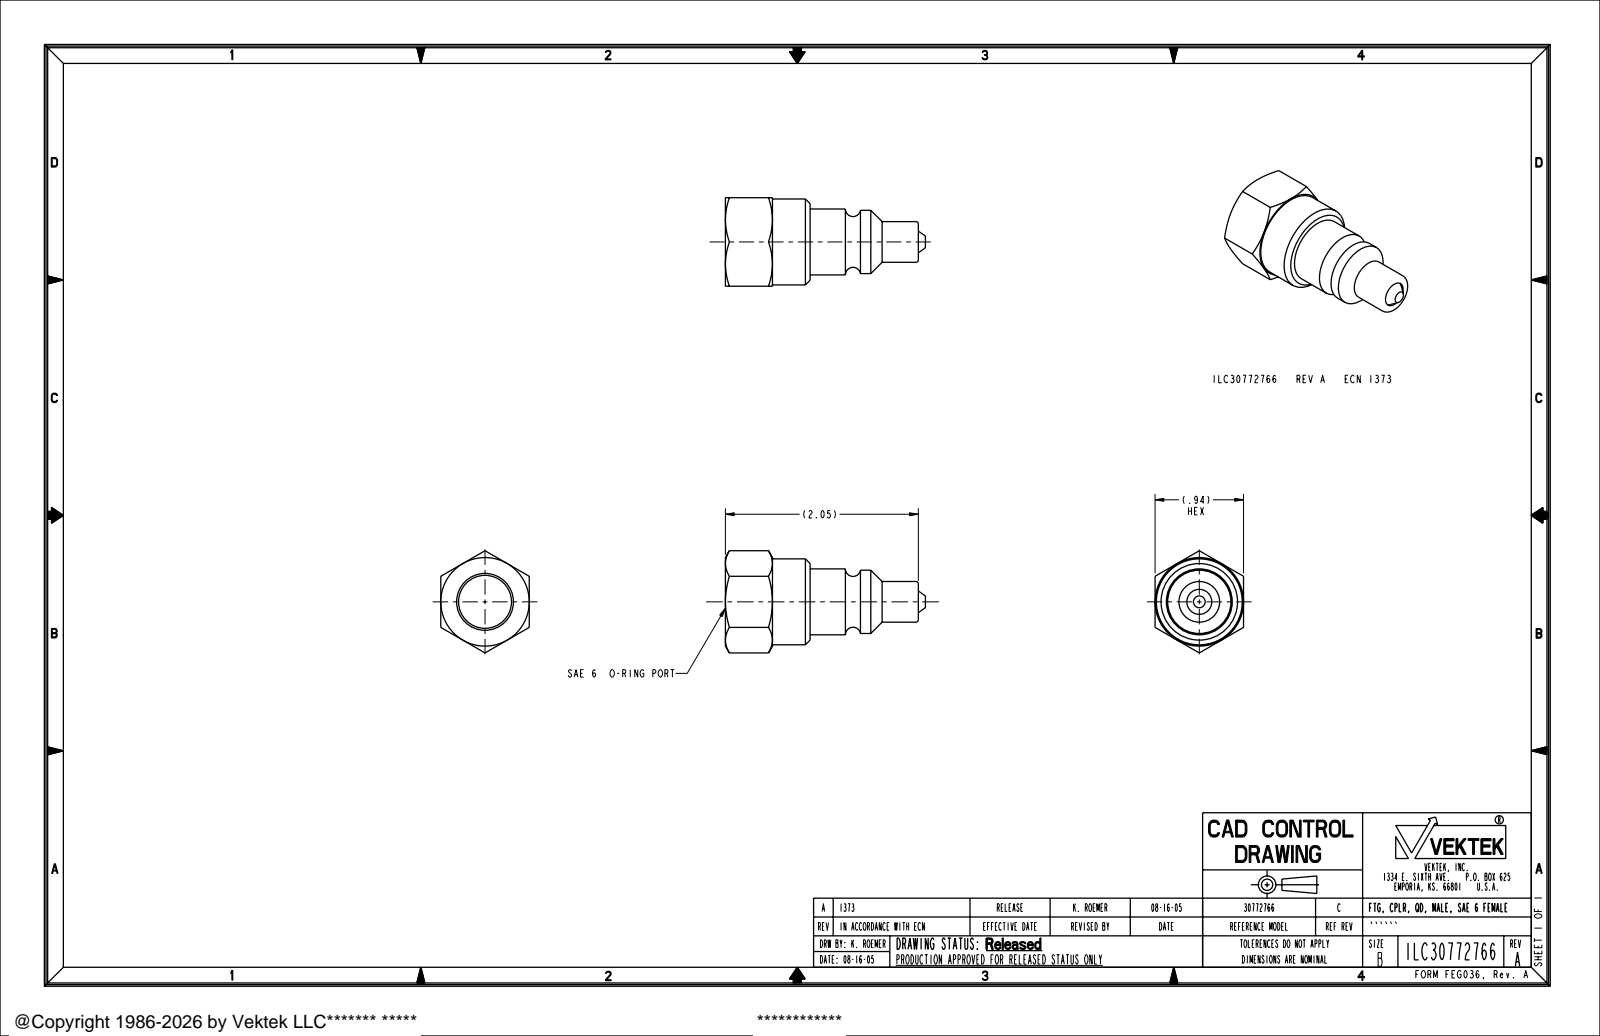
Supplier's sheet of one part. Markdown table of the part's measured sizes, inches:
| quantity | value |
| --- | --- |
| part name | ILC30772766 |
| STEP written by | PRO/ENGINEER BY PARAMETRIC TECHNOLOGY CORPORATION, 2004290 (AUTOMOTIVE_DESIGN_CC2) |
| units | inches |
| bodies | 1 solid, 48 faces (12 planar, 12 cylindrical, 24 other) |
| overall size | 2.125 × 1.085 × 0.94 |
| volume | 0.798 in³ |
| surface area | 7.313 in² |
| round holes (diameter × count) | 0.265 × 1, 0.563 × 1 |
| round bosses / shafts (diameter × count) | 0.913 × 1, 0.7 × 1, 0.672 × 1, 0.432 × 1 |
| main face-to-face distances | 0.94, 0.609, 0.9, 0.291, 2.05, 1.441, 1.15, 0.5, 0.109, 0.4 |
